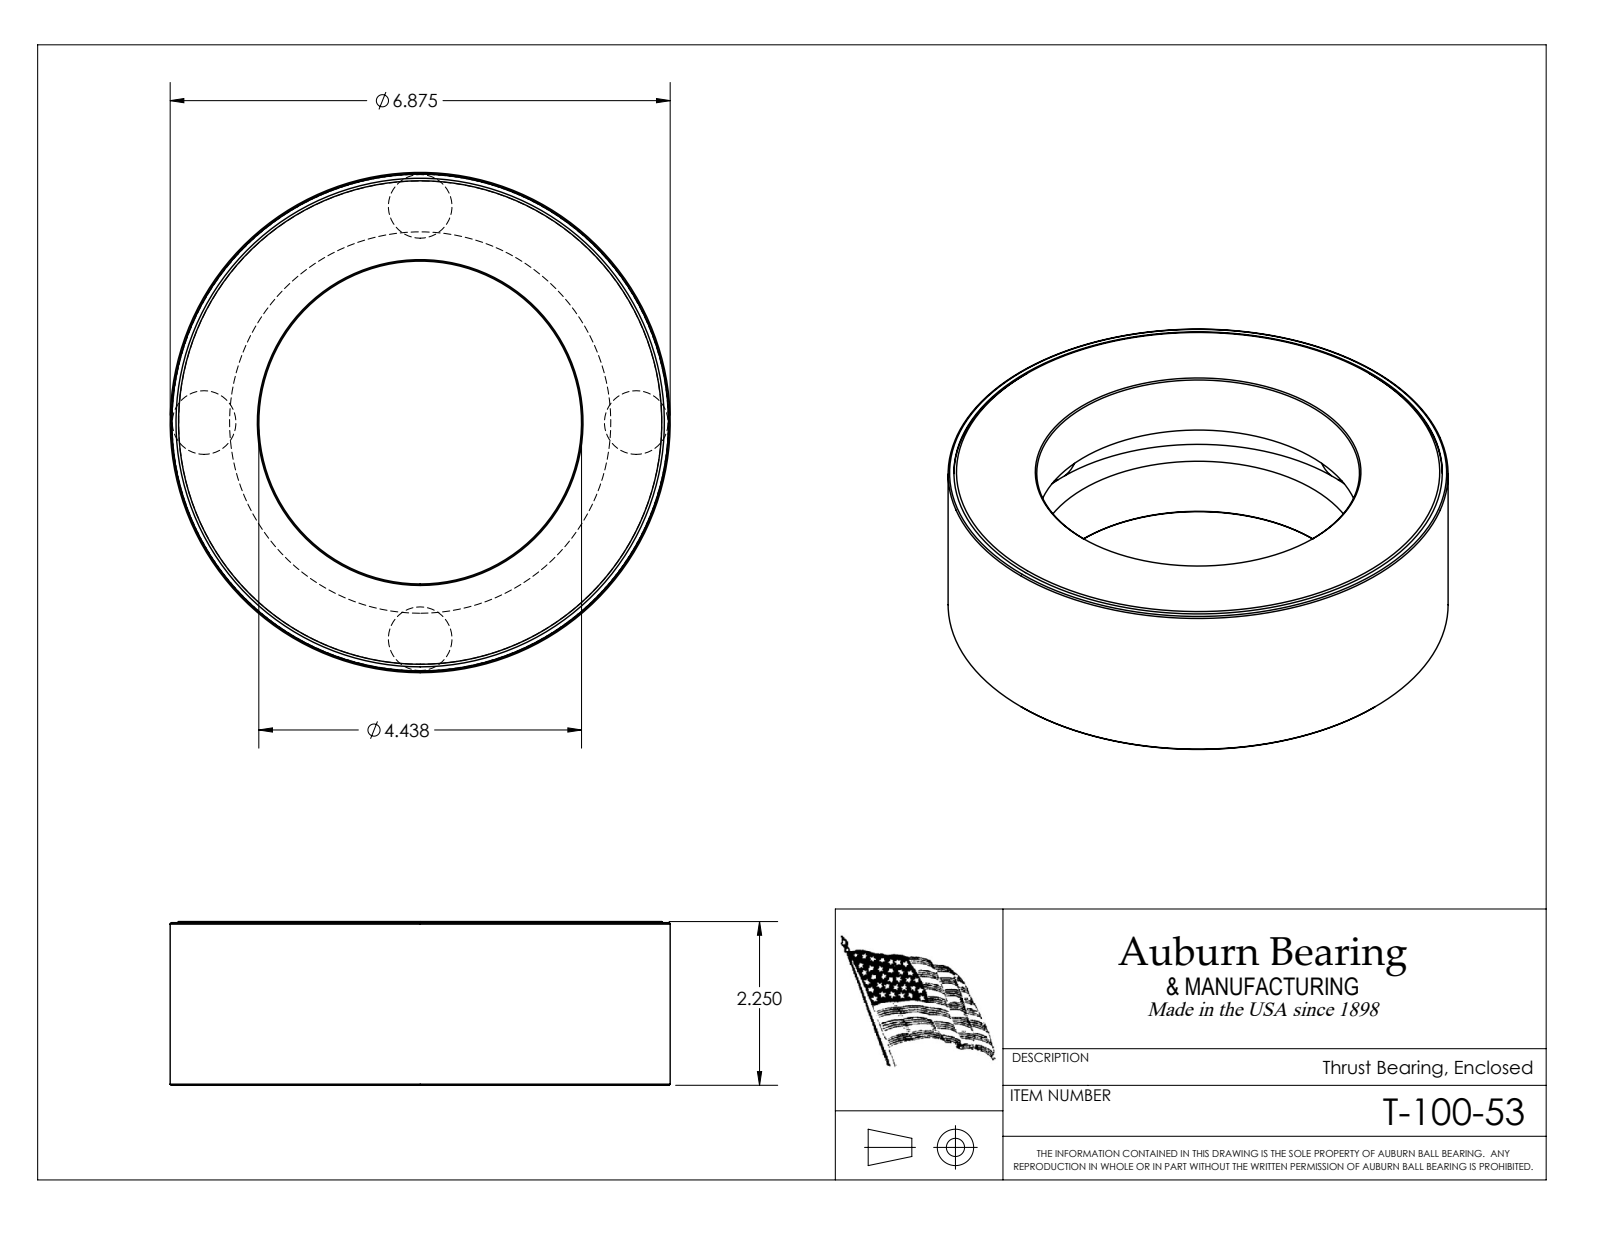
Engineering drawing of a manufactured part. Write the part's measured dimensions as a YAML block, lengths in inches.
part_name: "T-100-53"
step_written_by: "SolidWorks 2016 (CONFIG_CONTROL_DESIGN)"
units: inches
bodies: {solids: 6, faces: 28, planar: 9, cylindrical: 7, other: 12}
overall_size: [6.875, 6.875, 2.25]
volume: 35.59
surface_area: 220.4
round_holes:
  - {diameter: 4.437, count: 1}
  - {diameter: 6.715, count: 1}
  - {diameter: 6.835, count: 1}
round_bosses_or_shafts:
  - {diameter: 6.875, count: 1}
  - {diameter: 6.821, count: 1}
face_to_face_distances: [2.25, 0.863, 1.387, 0.525, 2.215, 2.235, 1.352, 1.372, 0.828, 0.848]
